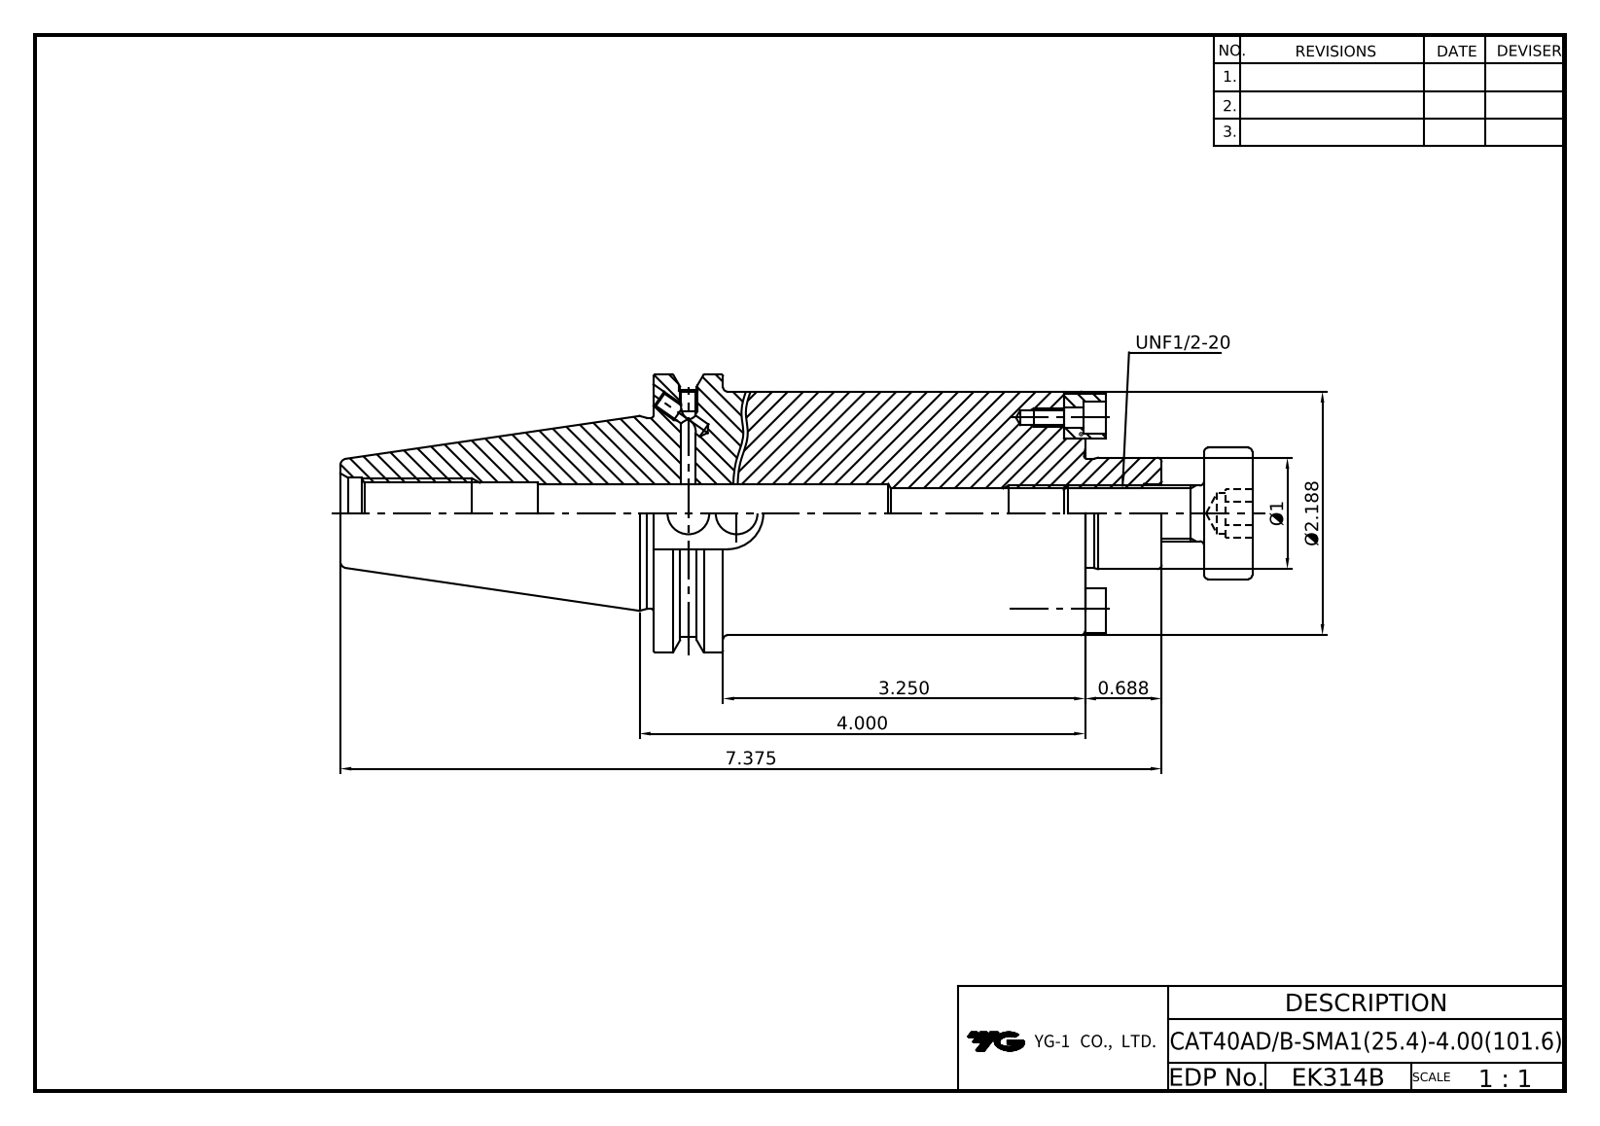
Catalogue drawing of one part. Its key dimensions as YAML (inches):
part_name: "LO-CAT40ADB-SMA25.4-101.6; HEX'' WRENCH BOLT-UNC#8-32x3_8L; DRIVE KEY-9.52x9.52x10.2; COLLAR BOLT-UNF1_2-20x32L"
step_written_by: "Autodesk Inventor 2022 (AUTOMOTIVE_DESIGN)"
units: inches
bodies: {solids: 6, faces: 171, planar: 85, cylindrical: 48, other: 38}
overall_size: [8.367, 2.5, 2.405]
volume: 18.85
surface_area: 72.31
round_holes:
  - {diameter: 0.128, count: 4}
  - {diameter: 0.13, count: 2}
  - {diameter: 0.157, count: 2}
  - {diameter: 0.165, count: 2}
  - {diameter: 0.177, count: 2}
  - {diameter: 0.295, count: 2}
  - {diameter: 0.375, count: 2}
  - {diameter: 0.446, count: 1}
  - {diameter: 0.512, count: 1}
  - {diameter: 0.527, count: 1}
  - {diameter: 0.531, count: 1}
  - {diameter: 0.642, count: 1}
round_bosses_or_shafts:
  - {diameter: 0.27, count: 2}
  - {diameter: 0.164, count: 2}
  - {diameter: 2.5, count: 1}
  - {diameter: 2.188, count: 1}
  - {diameter: 1.717, count: 1}
  - {diameter: 1.181, count: 1}
  - {diameter: 1, count: 1}
  - {diameter: 0.5, count: 1}
partial_cylinders:
  - {radius: 0.187, count: 2}
  - {radius: 0.322, count: 1}
  - {radius: 1.108, count: 1}
face_to_face_distances: [3.875, 5.555, 1.68, 5.122, 1.246, 0.433, 0.375, 3.687, 0.188, 1.434]
hole_center_spacings: [0.821, 1.642]
